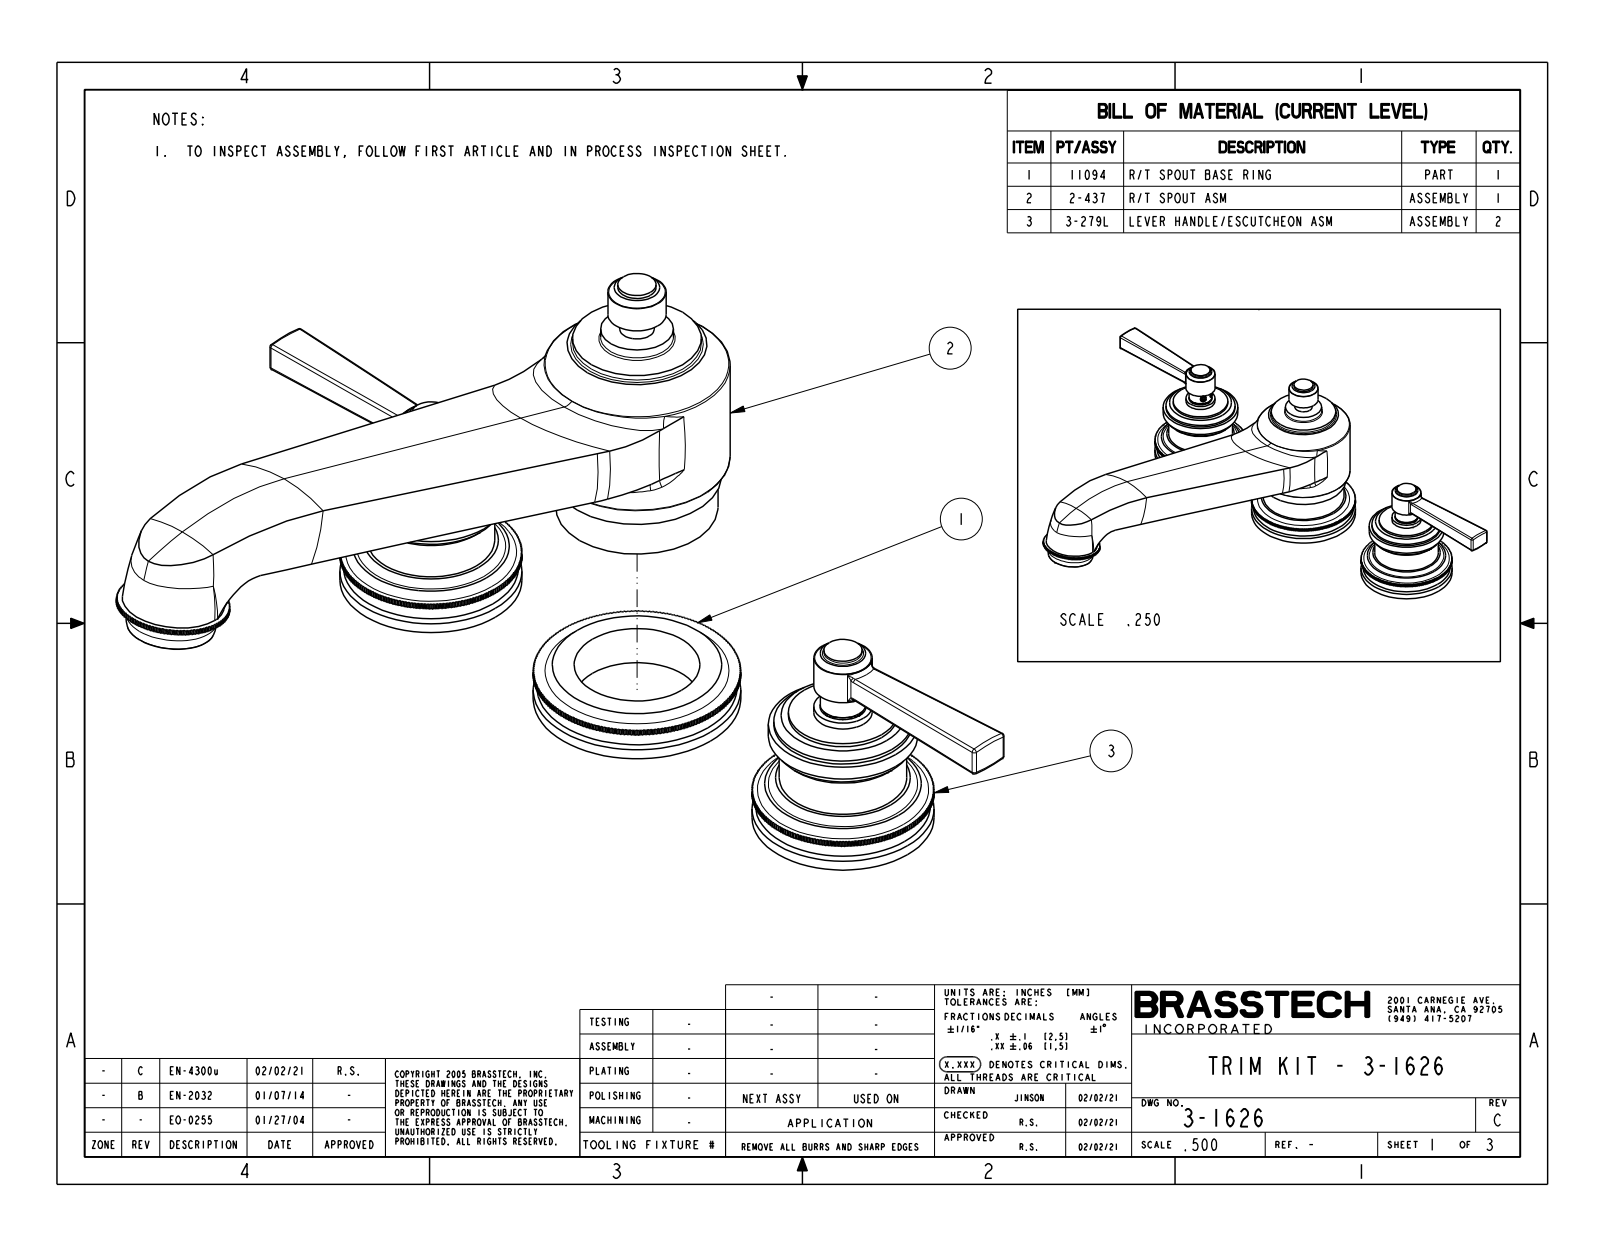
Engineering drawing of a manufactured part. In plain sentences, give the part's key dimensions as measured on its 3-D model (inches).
The part is named "3-1626". Its 3-D file was written by "CREO PARAMETRIC BY PTC INC, 2018400 (CONFIG_CONTROL_DESIGN)". It is 3 solids with 2198 faces: 1331 planar, 716 cylindrical and 151 other. Overall it measures 13.7 by 11.211 by 4.645 inches. Its volume is 46.15 cubic inches and its surface area 148.7 square inches. Round bosses or shafts: 3 of diameter 0.8, 3 of diameter 0.525, 2 of diameter 2.5, 2 of diameter 2.4, 2 of diameter 2.05, 2 of diameter 1.9, 2 of diameter 1.75, 2 of diameter 1.5. Partial cylindrical surfaces (rounded edges, fillets, slot ends): 4 of radius 0.04, 4 of radius 0.055, 1 of radius 0.781. The main face-to-face distances are 1.3, 1.775, 0.2, 0.475, 0.4, 0.1, 1.375, 0.15, 3.42, 2.945.
